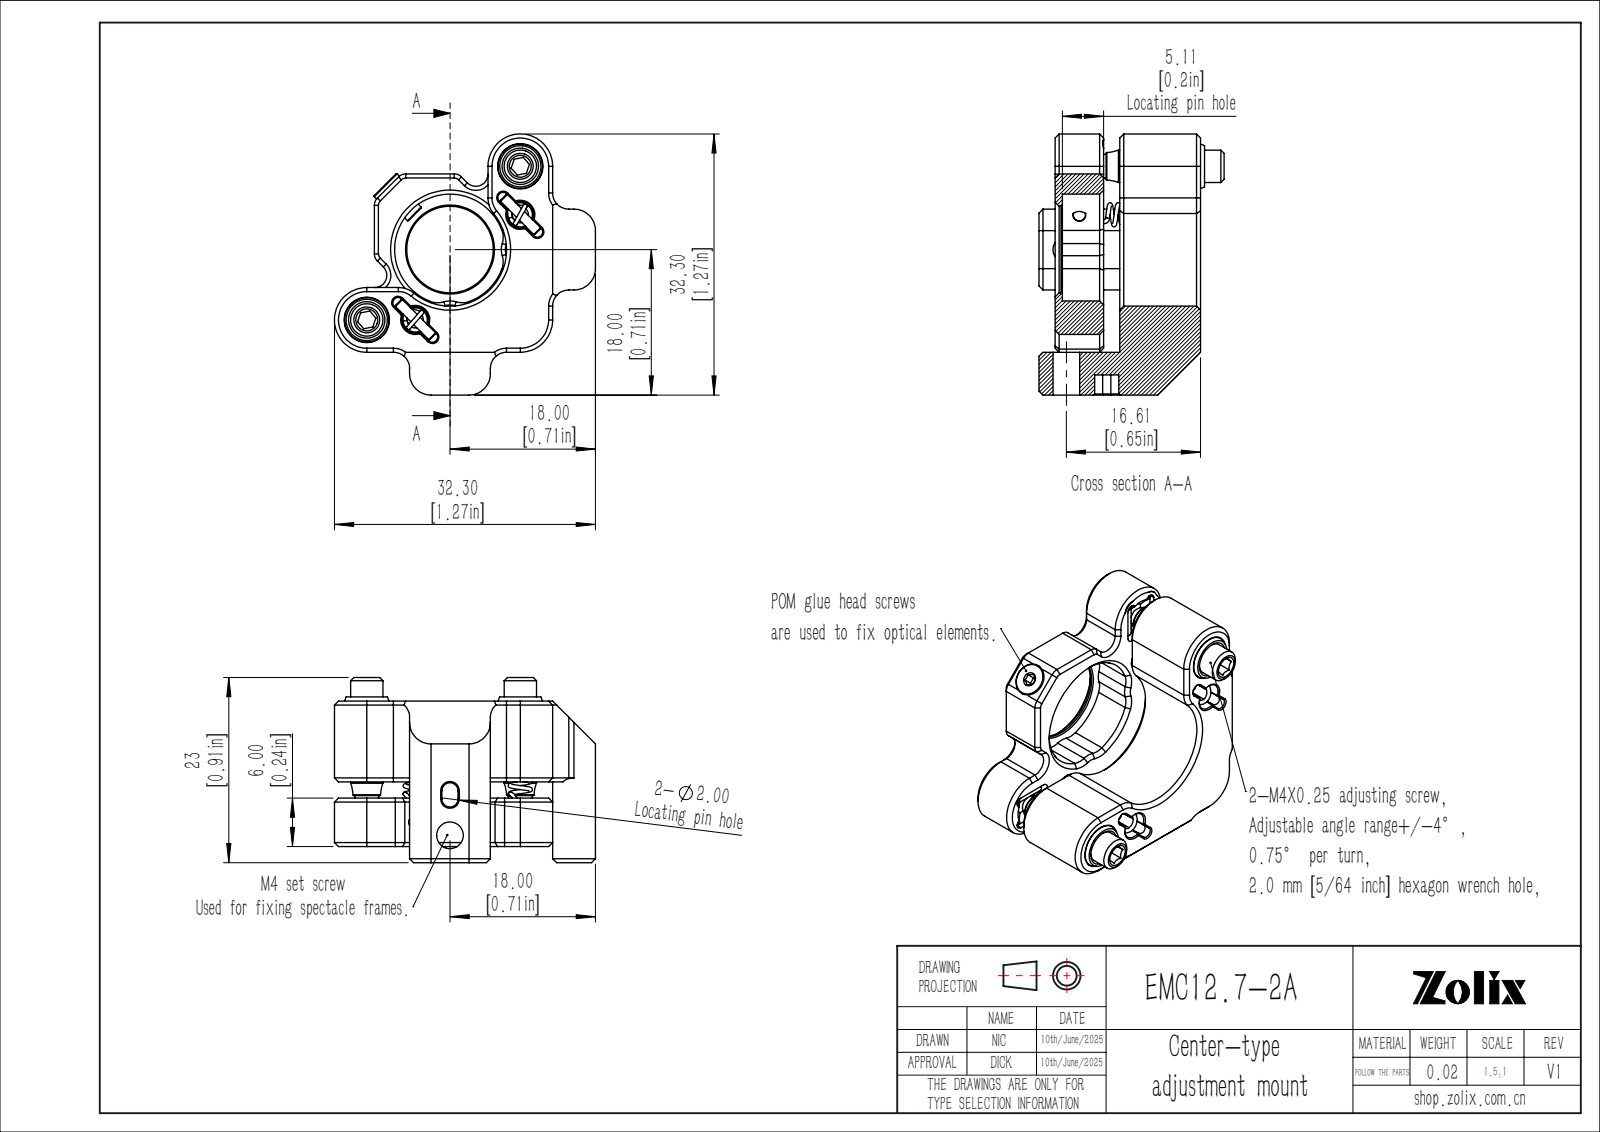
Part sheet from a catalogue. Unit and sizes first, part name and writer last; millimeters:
Units: millimetres
Overall size (bounding box): 32.3 × 32.3 × 22.91
Round holes (diameter × count): ⌀3.3 ×5, ⌀1.6 ×2, ⌀5.6 ×2, ⌀6.2 ×2, ⌀10.7 ×1
Round bosses / shafts (diameter × count): ⌀1.2 ×6, ⌀4 ×3, ⌀5.9 ×2, ⌀5.5 ×2, ⌀2.4 ×1
Partial cylindrical surfaces — rounded edges, fillets, slot ends (radius × count): R0.65 ×12, R2 ×8, R2.5 ×6, R1 ×4, R1.25 ×4, R1.5 ×4, R2.65 ×4, R4 ×3
Main face-to-face distances: 8, 2, 10, 6, 18, 12, 5.3, 13.3, 20, 14.05
Hole centre spacings: 4.59, 6, 9.7, 13.48, 23.02, 18.38, 26.87
Bodies: 0 solids, 514 faces (185 planar, 127 cylindrical, 202 other)
Part name (STEP PRODUCT): EMC12.7-2A
STEP written by: SolidWorks 2020 (CONFIG_CONTROL_DESIGN)
